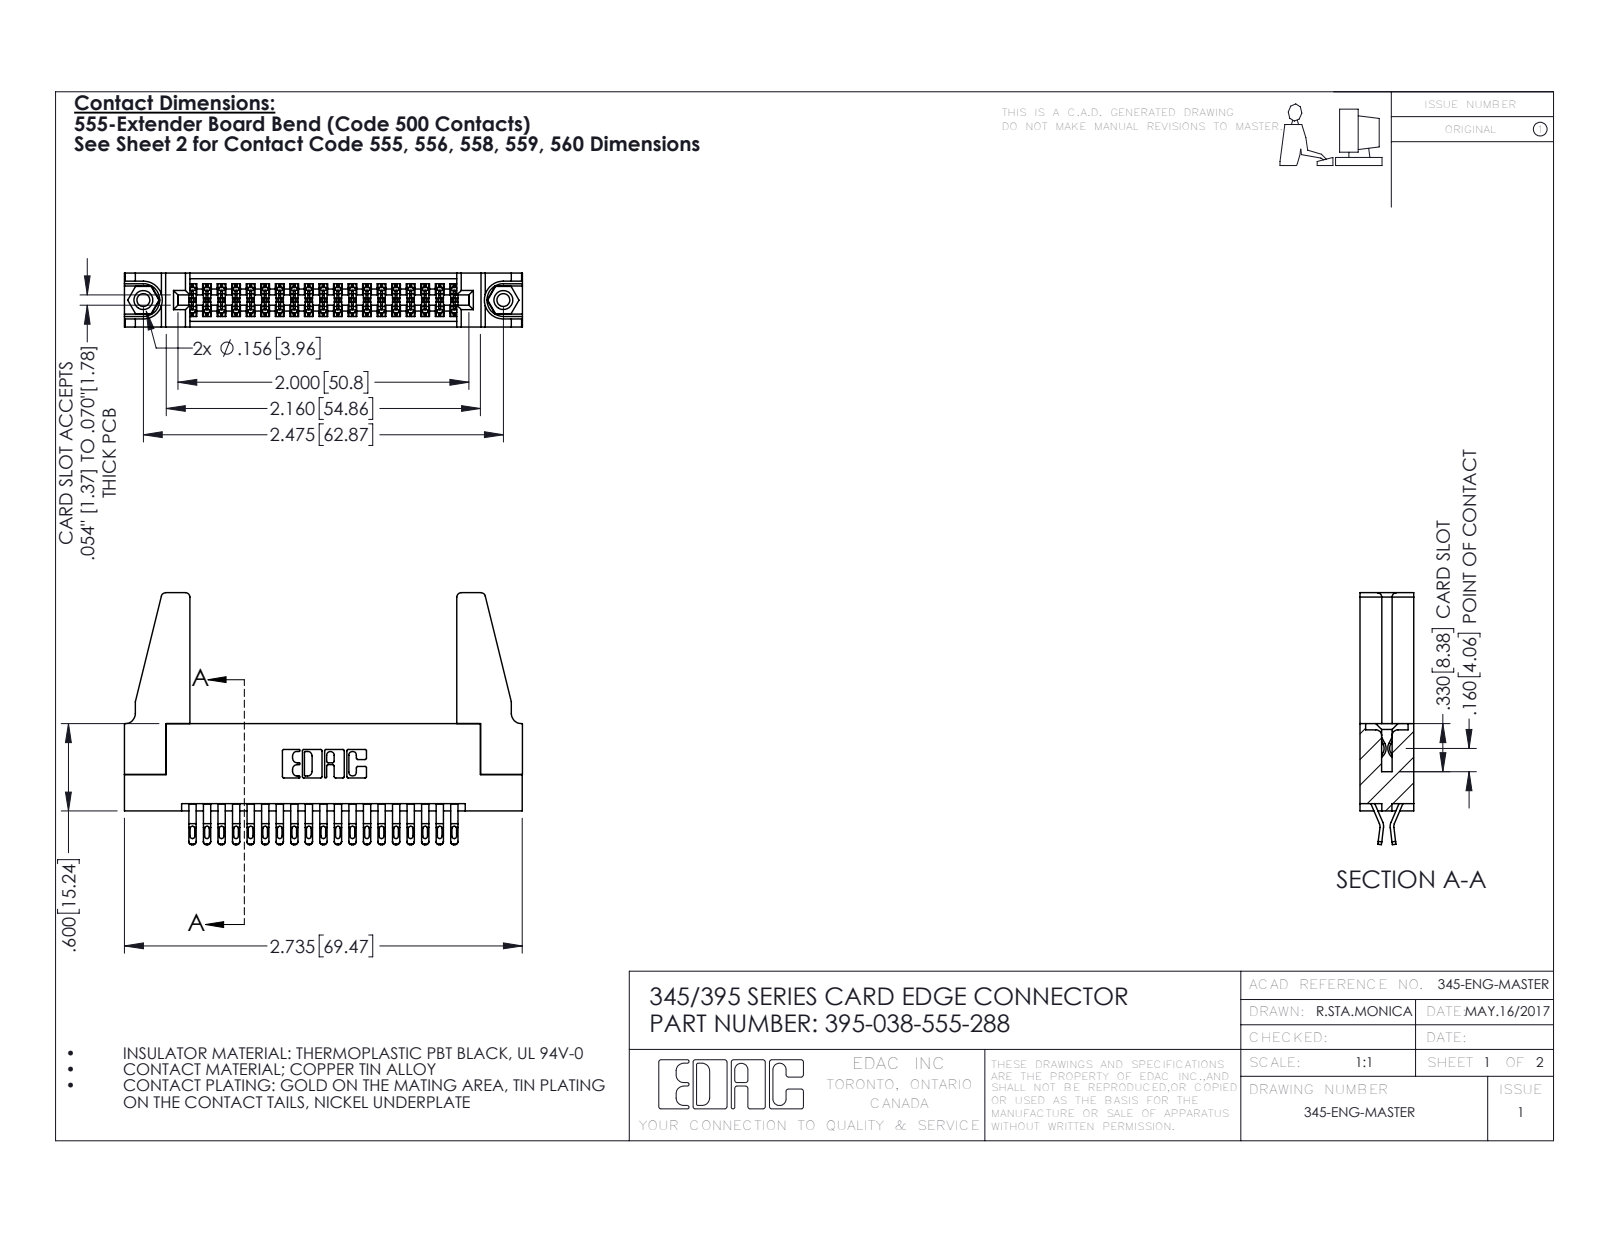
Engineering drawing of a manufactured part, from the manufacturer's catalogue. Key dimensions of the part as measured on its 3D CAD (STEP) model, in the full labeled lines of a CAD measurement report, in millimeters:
Part name (STEP PRODUCT): 345-250-001_345-250-001-102; 395-038-555-288; 345-292-001_555 Tail; 345 Part_Flush Mounting Lugs - 0.156 Dia-TH (+1 more)
STEP written by: SolidWorks 2016 (CONFIG_CONTROL_DESIGN)
Units: millimetres
Bodies: 43 solids, 2378 faces (1330 planar, 1032 cylindrical, 16 other)
Overall size (bounding box): 69.5 × 44 × 9.4
Volume: 9 900 mm³ · Surface area: 12 880 mm²
Round holes (diameter × count): ⌀2.3 ×2, ⌀3.2 ×2, ⌀4 ×2, ⌀1.6 ×1
Round bosses / shafts (diameter × count): ⌀3.9 ×2
Partial cylindrical surfaces — rounded edges, fillets, slot ends (radius × count): R0.4 ×95, R0.5 ×76, R0.2 ×57, R0.3 ×22, R0.8 ×8, R0.2 ×6, R0.8 ×6, R0.7 ×3
Main face-to-face distances: 9.4, 1.8, 7.6, 5.1, 0.6, 2.5, 6.9, 5.7, 4.4, 3.8
Hole centre spacings: 6.9, 56.9, 62.9
